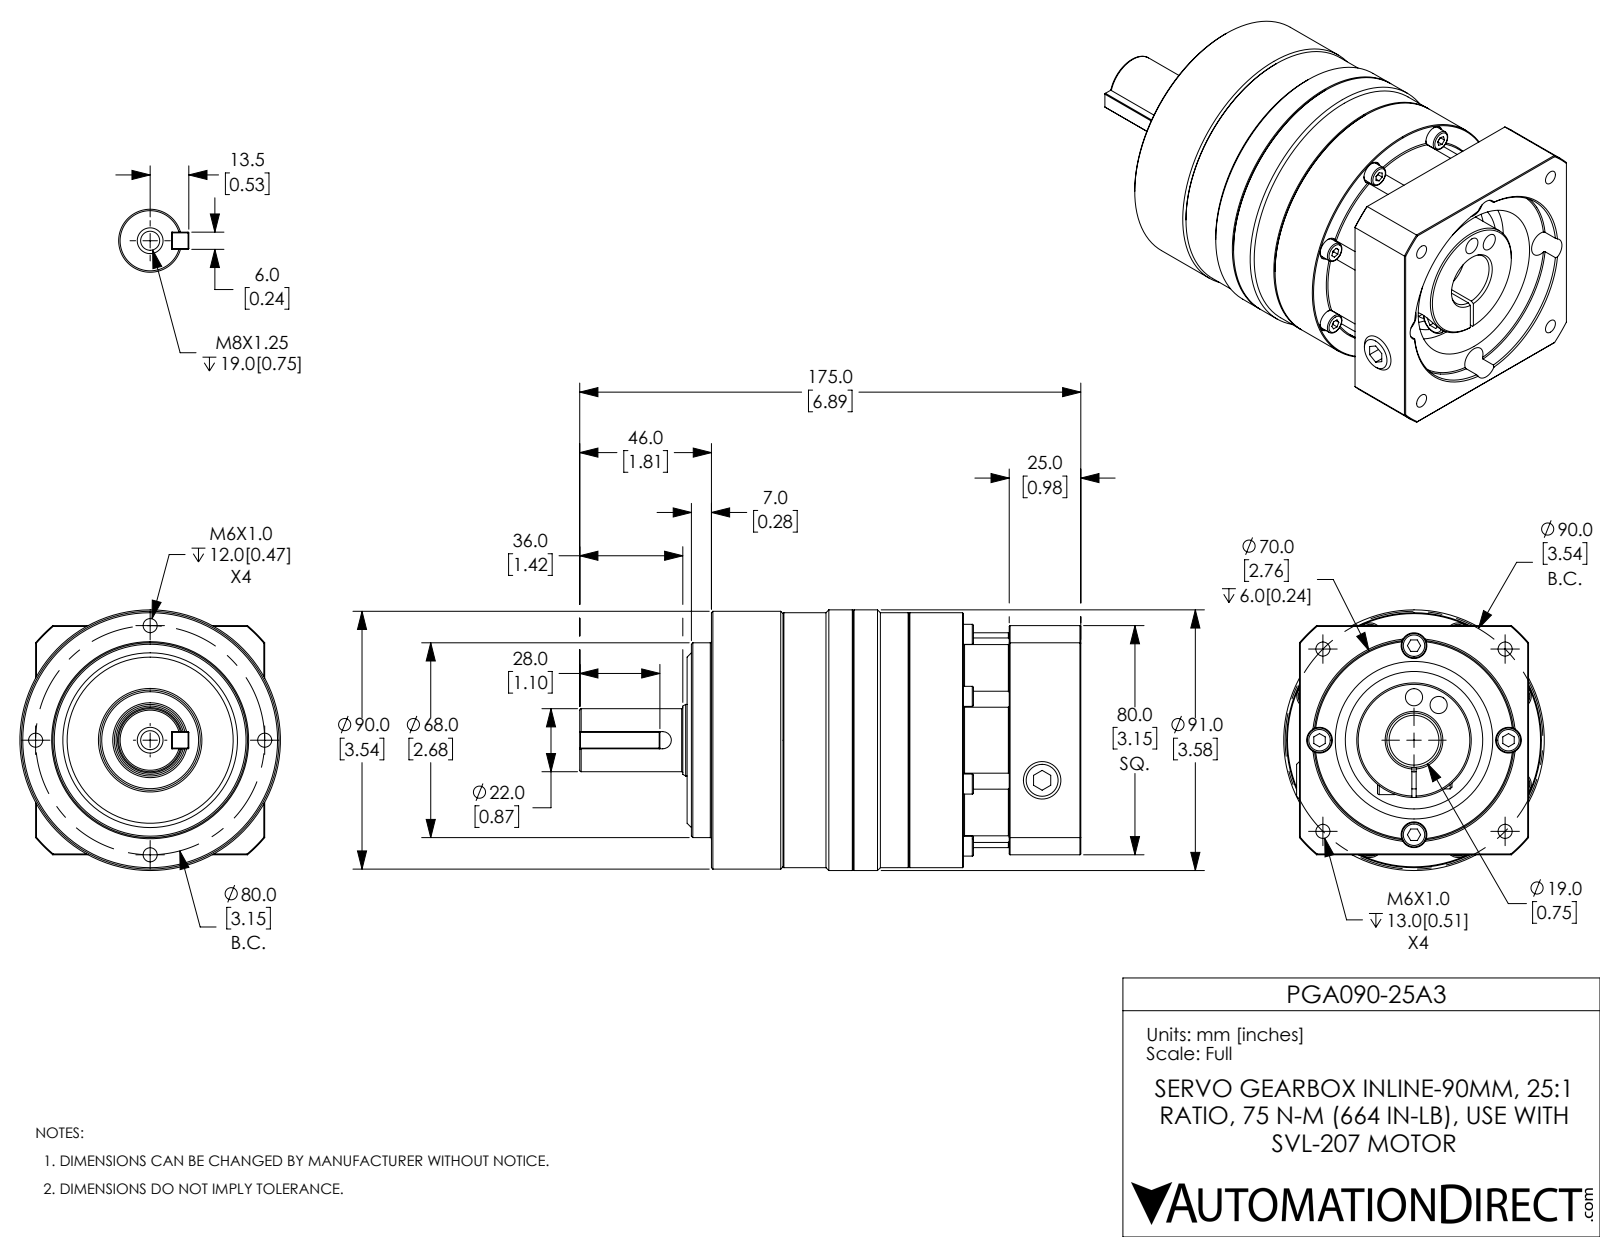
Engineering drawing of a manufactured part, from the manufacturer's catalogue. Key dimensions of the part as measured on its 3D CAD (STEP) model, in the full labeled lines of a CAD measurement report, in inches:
Part name (STEP PRODUCT): PGA090-25A3
STEP written by: SolidWorks 2019 (CONFIG_CONTROL_DESIGN)
Units: inches
Bodies: 1 solid, 471 faces (179 planar, 126 cylindrical, 166 other)
Overall size (bounding box): 6.89 × 3.583 × 3.583
Volume: 46.74 in³ · Surface area: 116.2 in²
Round holes (diameter × count): ⌀0.194 ×8, ⌀0.315 ×8, ⌀0.354 ×4, ⌀0.236 ×2, ⌀0.256 ×1, ⌀0.262 ×1, ⌀0.413 ×1, ⌀0.748 ×1, ⌀1.89 ×1, ⌀2.165 ×1, ⌀2.756 ×1
Round bosses / shafts (diameter × count): ⌀0.276 ×8, ⌀0.335 ×4, ⌀3.583 ×1, ⌀3.543 ×1, ⌀3.504 ×1, ⌀2.953 ×1, ⌀2.677 ×1, ⌀1.575 ×1
Partial cylindrical surfaces — rounded edges, fillets, slot ends (radius × count): R0.097 ×1, R0.118 ×1, R0.217 ×1, R2.067 ×1
Main face-to-face distances: 3.15, 5.079, 4.094, 0.984, 5.413, 0.335, 0.236, 4.429, 0.748, 0.63
Hole centre spacings: 0.615, 0.622, 0.681, 1.206, 1.254, 1.293, 1.575, 1.613
